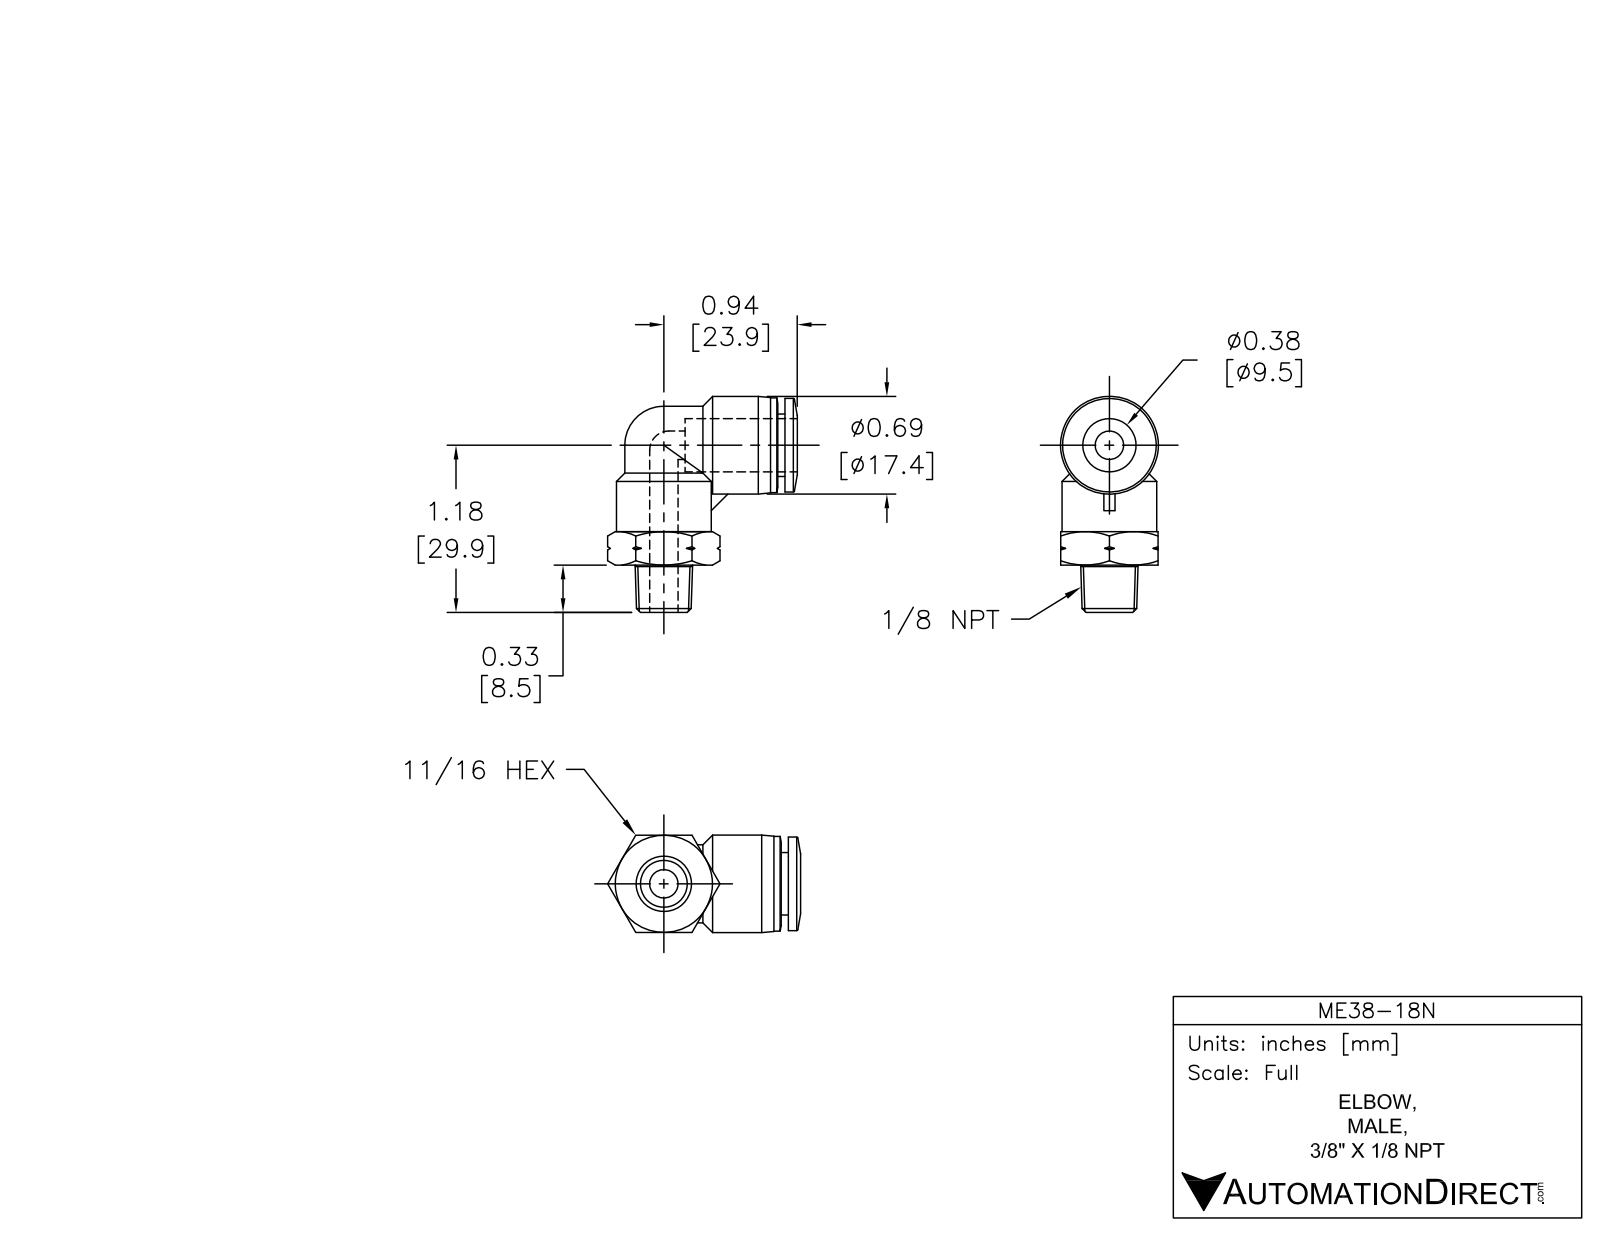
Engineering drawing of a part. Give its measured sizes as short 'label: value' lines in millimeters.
name: ME38-18N
written by: SolidWorks 2015 (AUTOMOTIVE_DESIGN)
unit: mm
bodies: 1 solid, 86 faces (16 planar, 20 cylindrical, 50 other)
size: 38.8 × 34.6 × 17.5
volume: 7 960 mm³; area: 4 434 mm²
holes: 2× ⌀5, 1× ⌀9.8
bosses: 2× ⌀17, 1× ⌀17.5, 1× ⌀16.8, 1× ⌀14, 1× ⌀11.2
rounds: 1× R7
face distances: 17.4, 1.3, 16.6, 17.9, 8.5, 14.5, 6, 7.7, 9.7, 2
